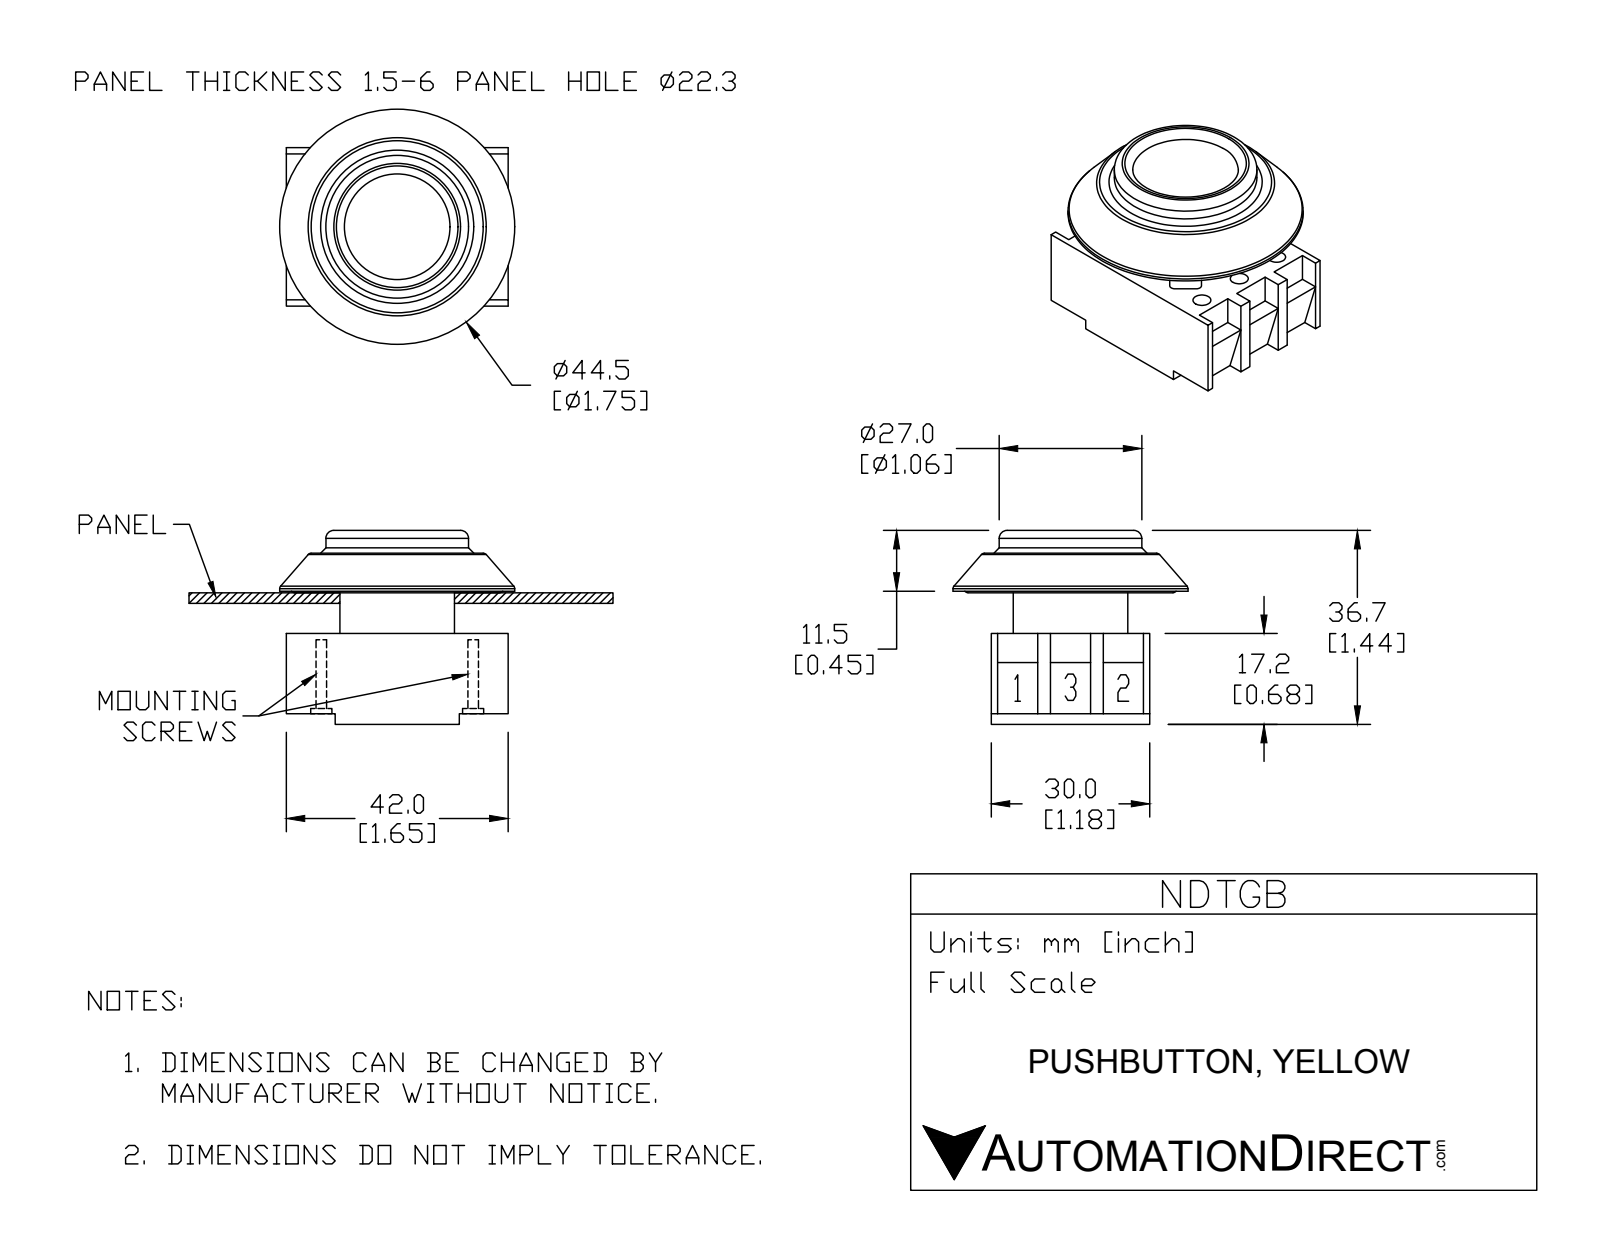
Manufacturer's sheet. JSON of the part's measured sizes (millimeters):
{"part_name": "NDTGB", "step_written_by": "SolidWorks 2015 (AUTOMOTIVE_DESIGN)", "units": "millimeters", "bodies": {"solids": 7, "faces": 217, "planar": 127, "cylindrical": 65, "other": 25}, "overall_size": [44.5, 44.5, 36.7], "volume_mm3": 25120, "surface_area_mm2": 16719, "round_holes": [[3.4, 6], [5, 6], [12.5, 1]], "round_bosses_or_shafts": [[4.6, 2], [4, 2], [44.5, 1], [27, 1], [21.7, 1]], "partial_cylinders_radius": [[1, 8], [8.7, 5], [11, 1]], "face_to_face_distances": [7.2, 15.2, 30, 10, 8, 7.5, 7.7, 10.3, 18, 23.2], "hole_center_spacings": [10, 17.52, 30.45, 28.76, 14.38, 20, 35.03]}
